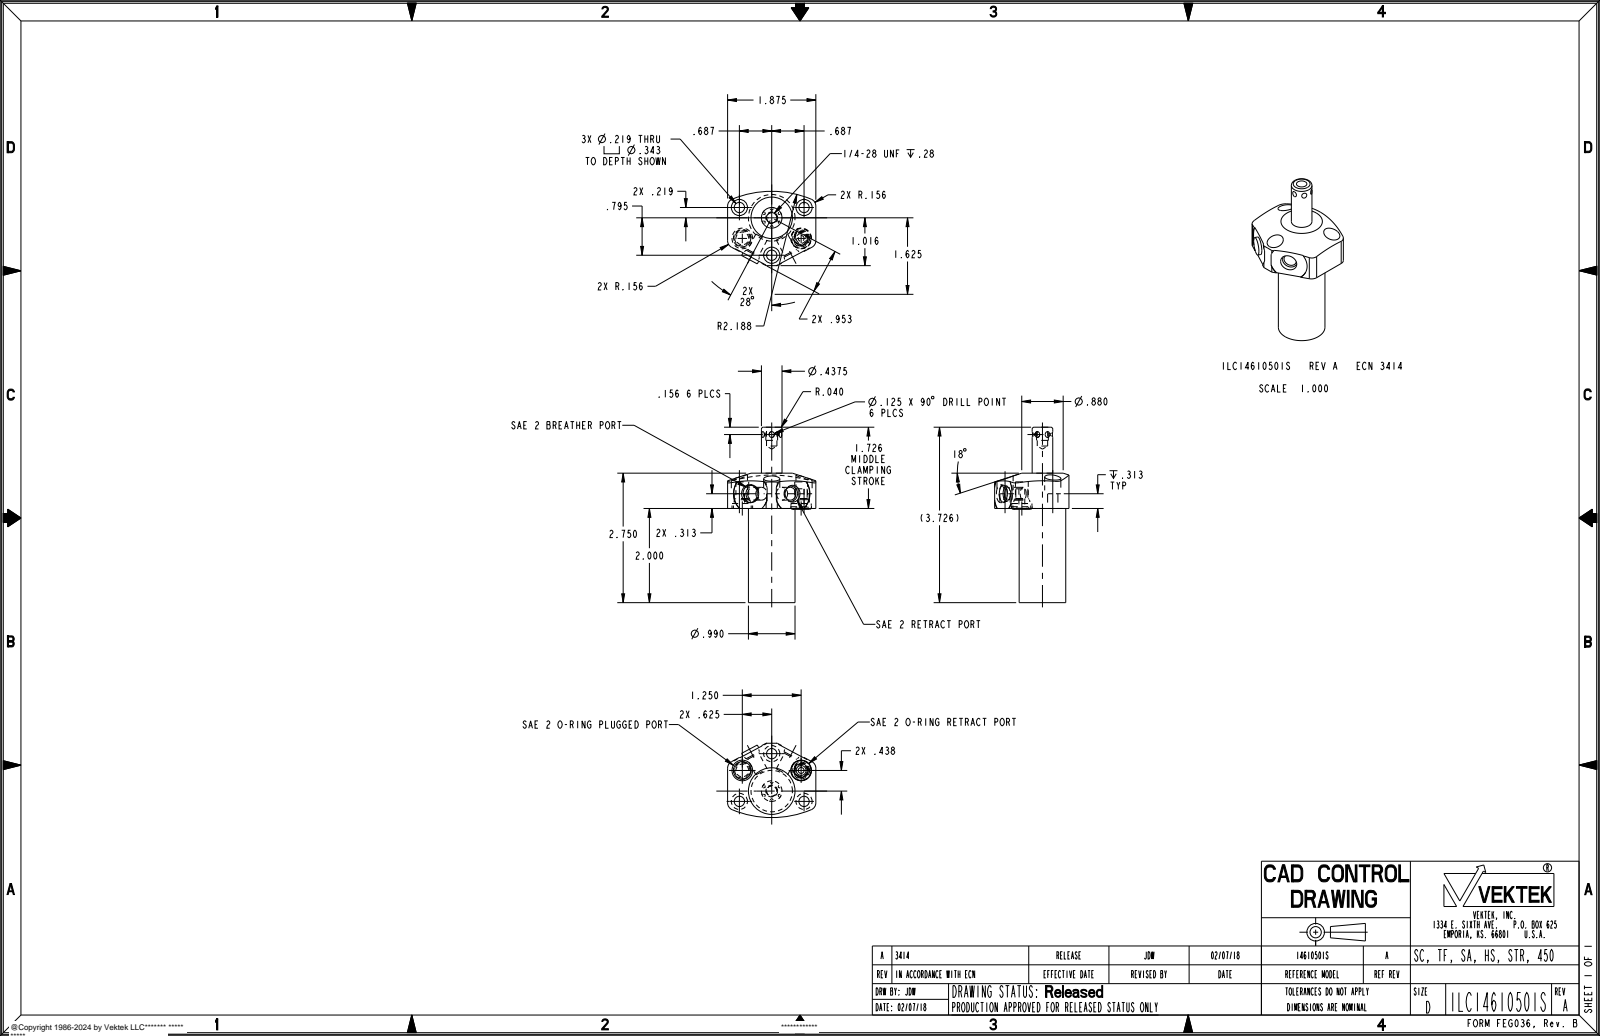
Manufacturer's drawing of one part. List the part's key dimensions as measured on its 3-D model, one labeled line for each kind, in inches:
Part name (STEP PRODUCT): ILC14610501S
STEP written by: PRO/ENGINEER BY PARAMETRIC TECHNOLOGY CORPORATION, 2013320 (AUTOMOTIVE_DESIGN)
Units: inches
Bodies: 1 solid, 127 faces (34 planar, 55 cylindrical, 38 other)
Overall size (bounding box): 3.726 × 1.875 × 1.579
Volume: 3.103 in³ · Surface area: 21.35 in²
Round holes (diameter × count): ⌀0.272 ×4, ⌀0.219 ×3, ⌀0.343 ×3, ⌀0.438 ×2, ⌀0.125 ×1, ⌀0.221 ×1
Round bosses / shafts (diameter × count): ⌀0.378 ×2, ⌀0.99 ×1, ⌀0.437 ×1, ⌀0.43 ×1, ⌀0.256 ×1, ⌀0.25 ×1, ⌀0.21 ×1
Partial cylindrical surfaces — rounded edges, fillets, slot ends (radius × count): R0.156 ×4, R0.412 ×2, R2.188 ×1
Main face-to-face distances: 2, 2.75, 0.75, 1.875, 0.105, 0.313, 2.105, 0.645, 2.313, 0.208
Hole centre spacings: 0.66, 0.72, 0.721, 0.763, 1.225, 1.468, 0.795, 1.25
